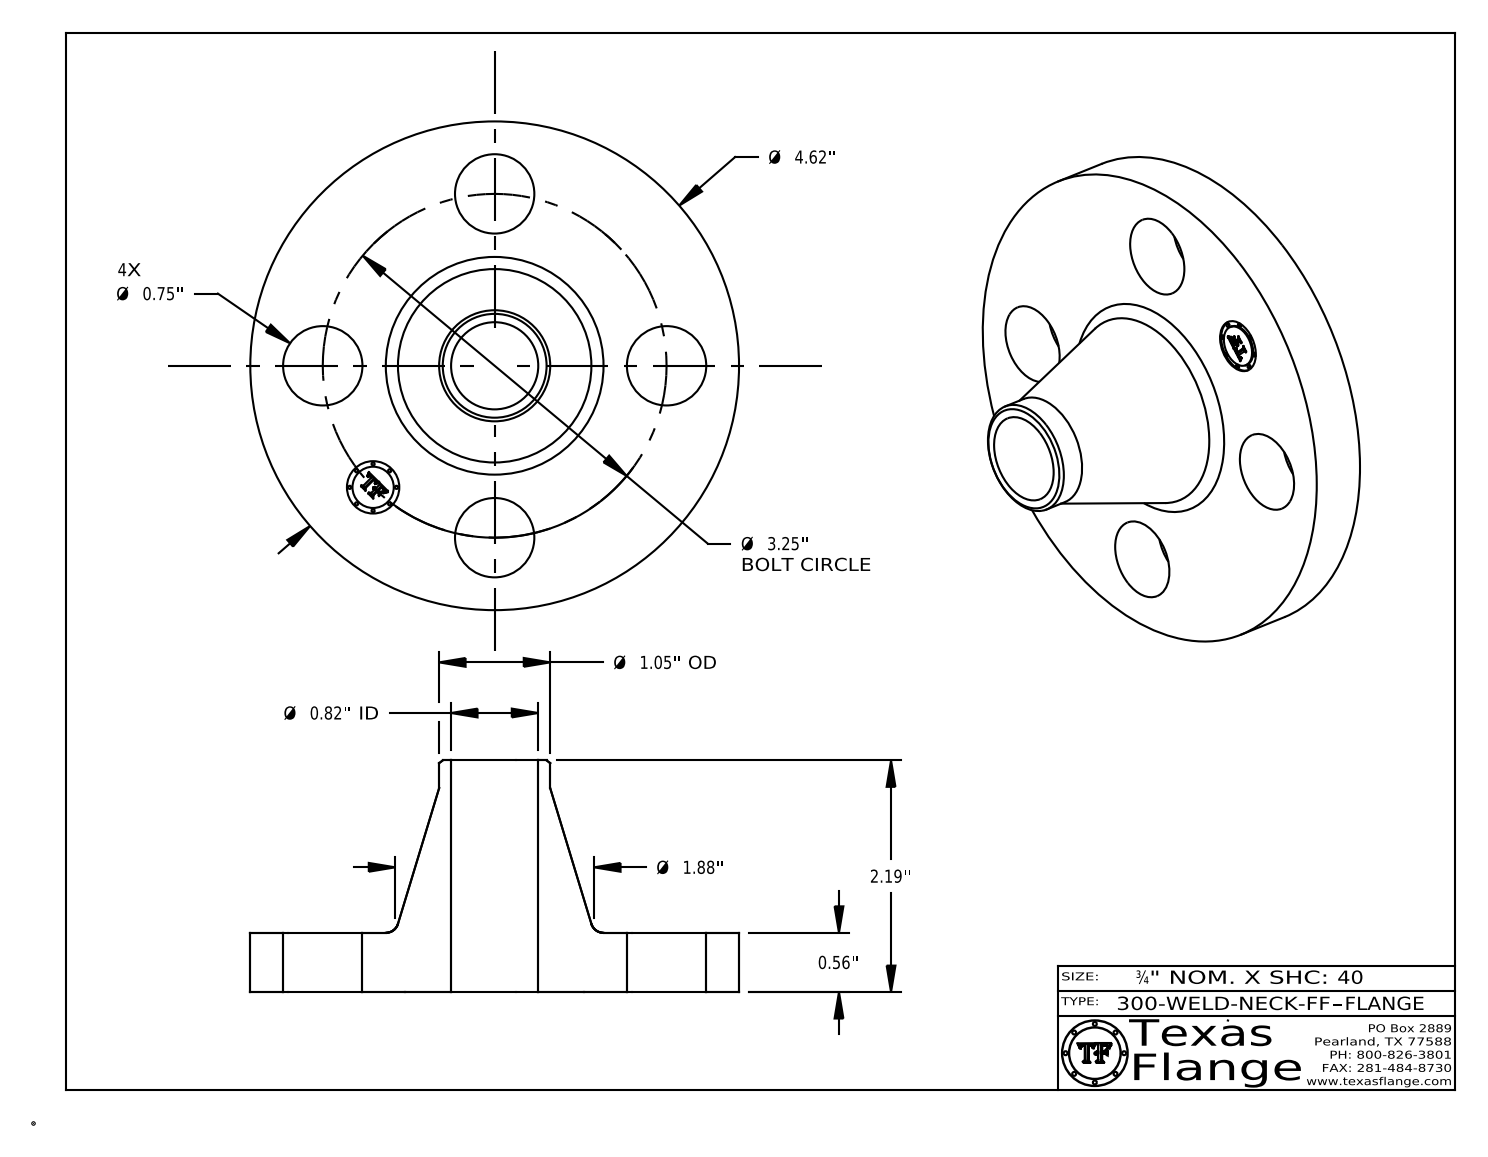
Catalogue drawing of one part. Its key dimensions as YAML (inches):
part_name: "300-WELD-NECK-FF"
step_written_by: "CATIA V5 STEP AP214 (AUTOMOTIVE_DESIGN)"
units: inches
bodies: {solids: 1, faces: 409, planar: 369, cylindrical: 34, other: 6}
overall_size: [4.62, 4.62, 2.19]
volume: 9.831
surface_area: 53.43
round_holes:
  - {diameter: 0.75, count: 4}
  - {diameter: 0.495, count: 1}
  - {diameter: 0.824, count: 1}
round_bosses_or_shafts:
  - {diameter: 0.03, count: 8}
  - {diameter: 4.62, count: 1}
  - {diameter: 1.05, count: 1}
  - {diameter: 0.39, count: 1}
face_to_face_distances: [0.56, 2.19, 1.63, 0.545, 0.015, 1.645, 0.148, 0.144, 0.027, 0.096]
hole_center_spacings: [1.625, 2.298, 1.244, 3.003, 3.25]
